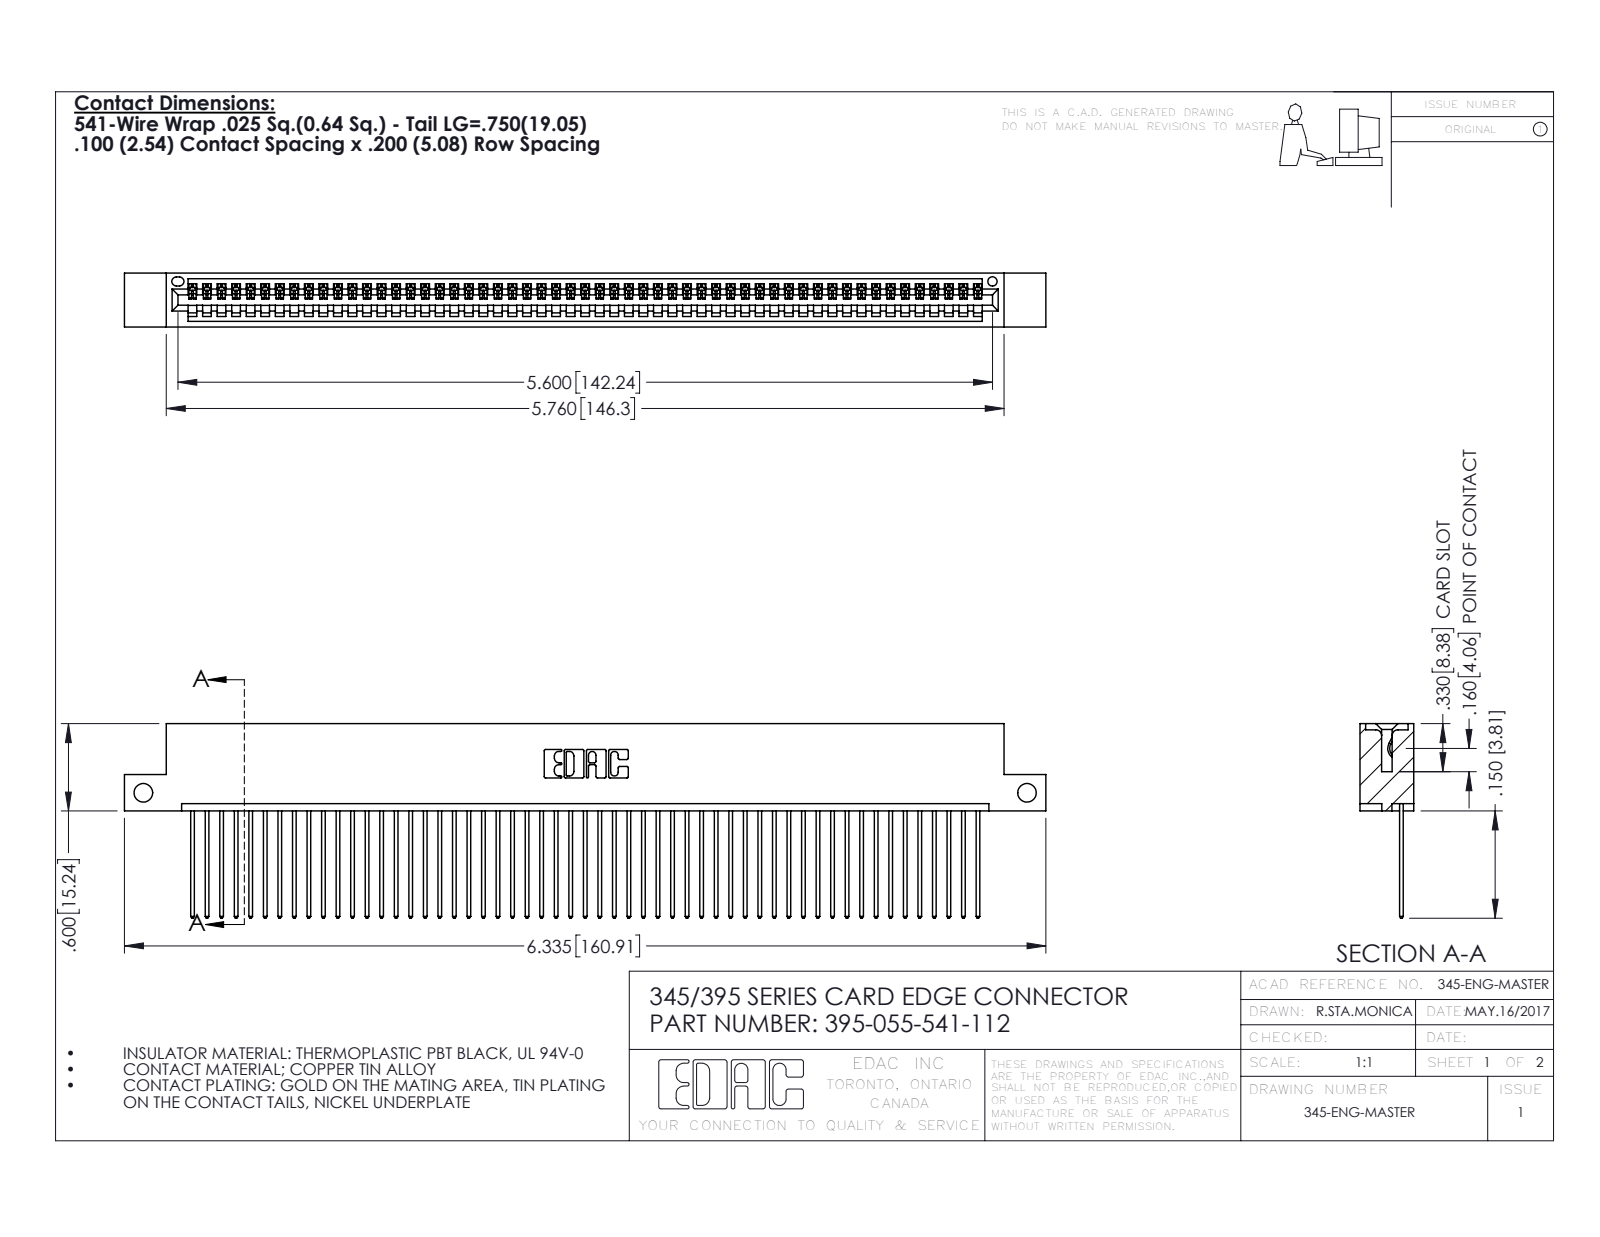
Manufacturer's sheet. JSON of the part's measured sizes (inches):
{"part_name": "395-055-541-112; 345-292-001_345-293-141; 345 Part_Flush Mounting Lugs - Side Mount", "step_written_by": "SolidWorks 2016 (CONFIG_CONTROL_DESIGN)", "units": "inches", "bodies": {"solids": 56, "faces": 3316, "planar": 2280, "cylindrical": 1036, "other": 0}, "overall_size": [6.335, 1.337, 0.37], "volume_in3": 0.945, "surface_area_in2": 33.6, "round_holes": [[0.128, 2], [0.064, 1]], "partial_cylinders_radius": [[0.006, 110], [0.01, 110], [0.01, 22], [0.007, 6], [0.031, 6], [0.026, 3], [0.031, 2], [0.04, 2]], "face_to_face_distances": [0.072, 0.298, 0.098, 0.272, 0.025, 0.37, 0.2, 0.225, 0.149, 0.072], "hole_center_spacings": [6.075]}
